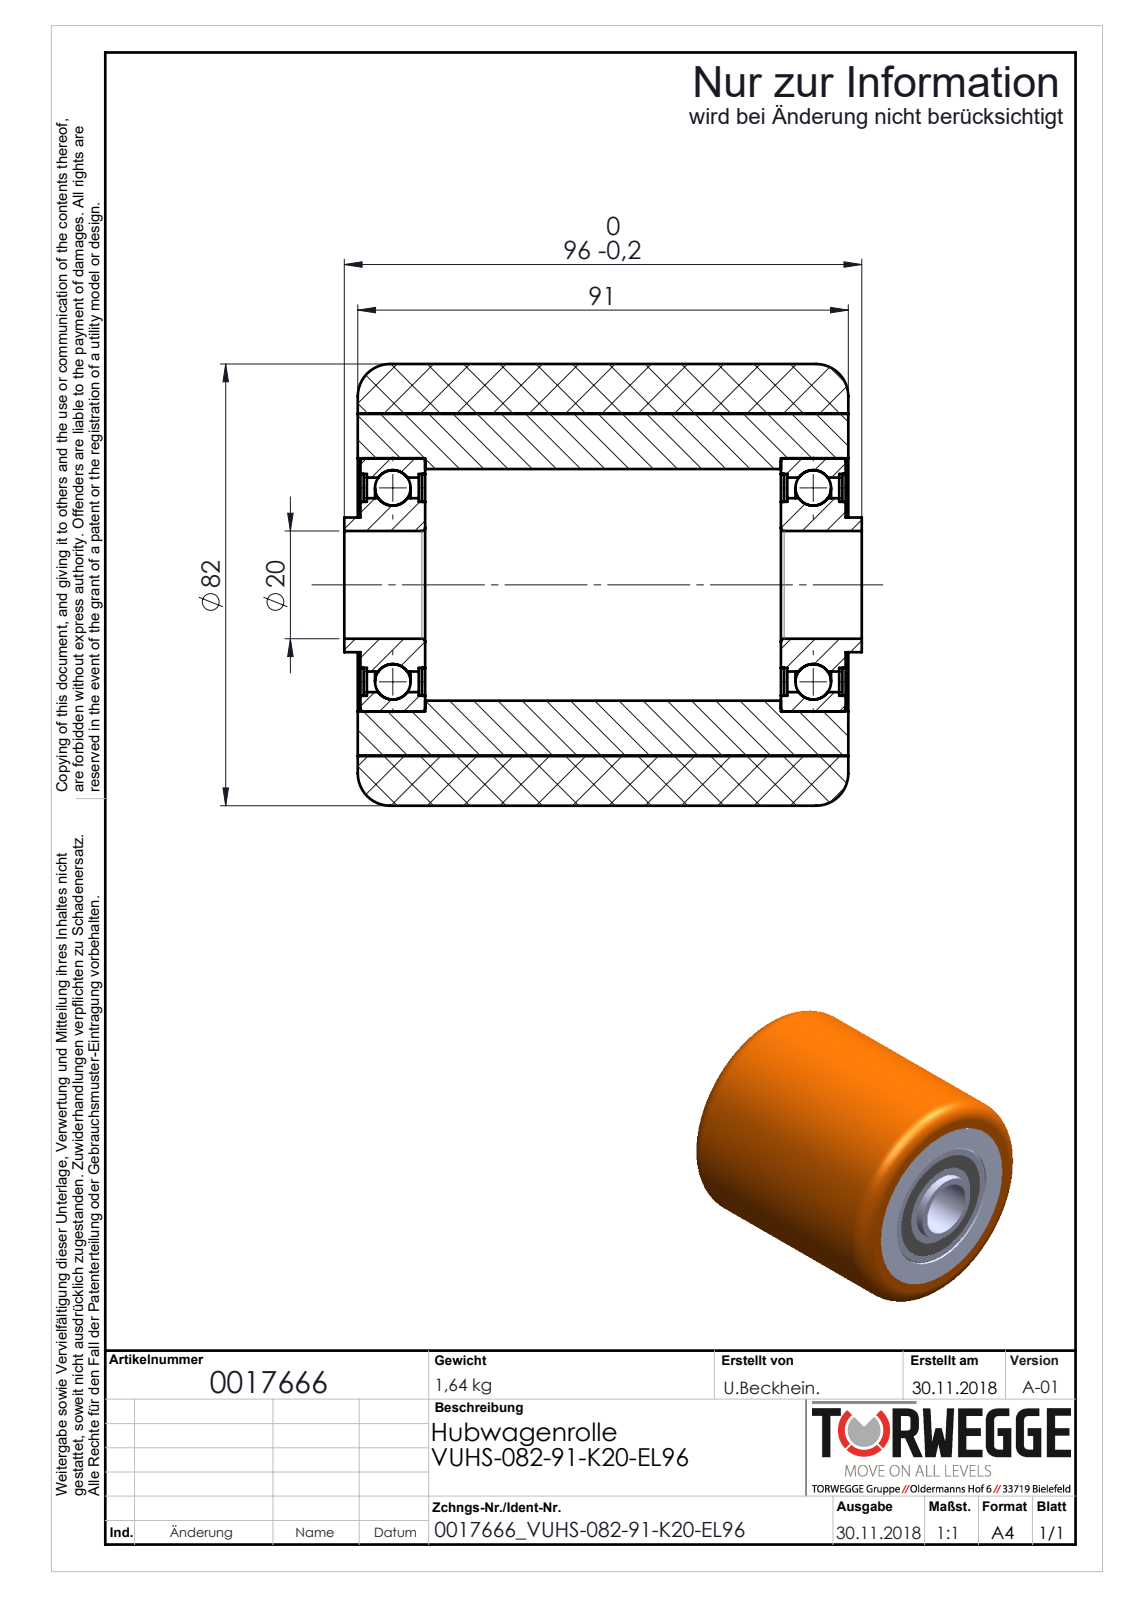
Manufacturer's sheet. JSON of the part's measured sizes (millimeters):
{"part_name": "0017666_VUHS-082-91-K20-EL96_(A-01)", "step_written_by": "SolidWorks 2018 (AUTOMOTIVE_DESIGN)", "units": "millimeters", "bodies": {"solids": 12, "faces": 140, "planar": 32, "cylindrical": 72, "other": 36}, "overall_size": [96, 82, 82], "volume_mm3": 368261, "surface_area_mm2": 104067, "round_holes": [[20, 1], [30.83, 1], [39.83, 1], [41.17, 1], [43, 1], [47, 1], [63.5, 1]], "round_bosses_or_shafts": [[82, 1], [32.17, 1], [25, 1]], "face_to_face_distances": [78, 12.5, 78.5, 0.59, 11.41, 0.5, 90.5, 12, 91, 66]}
